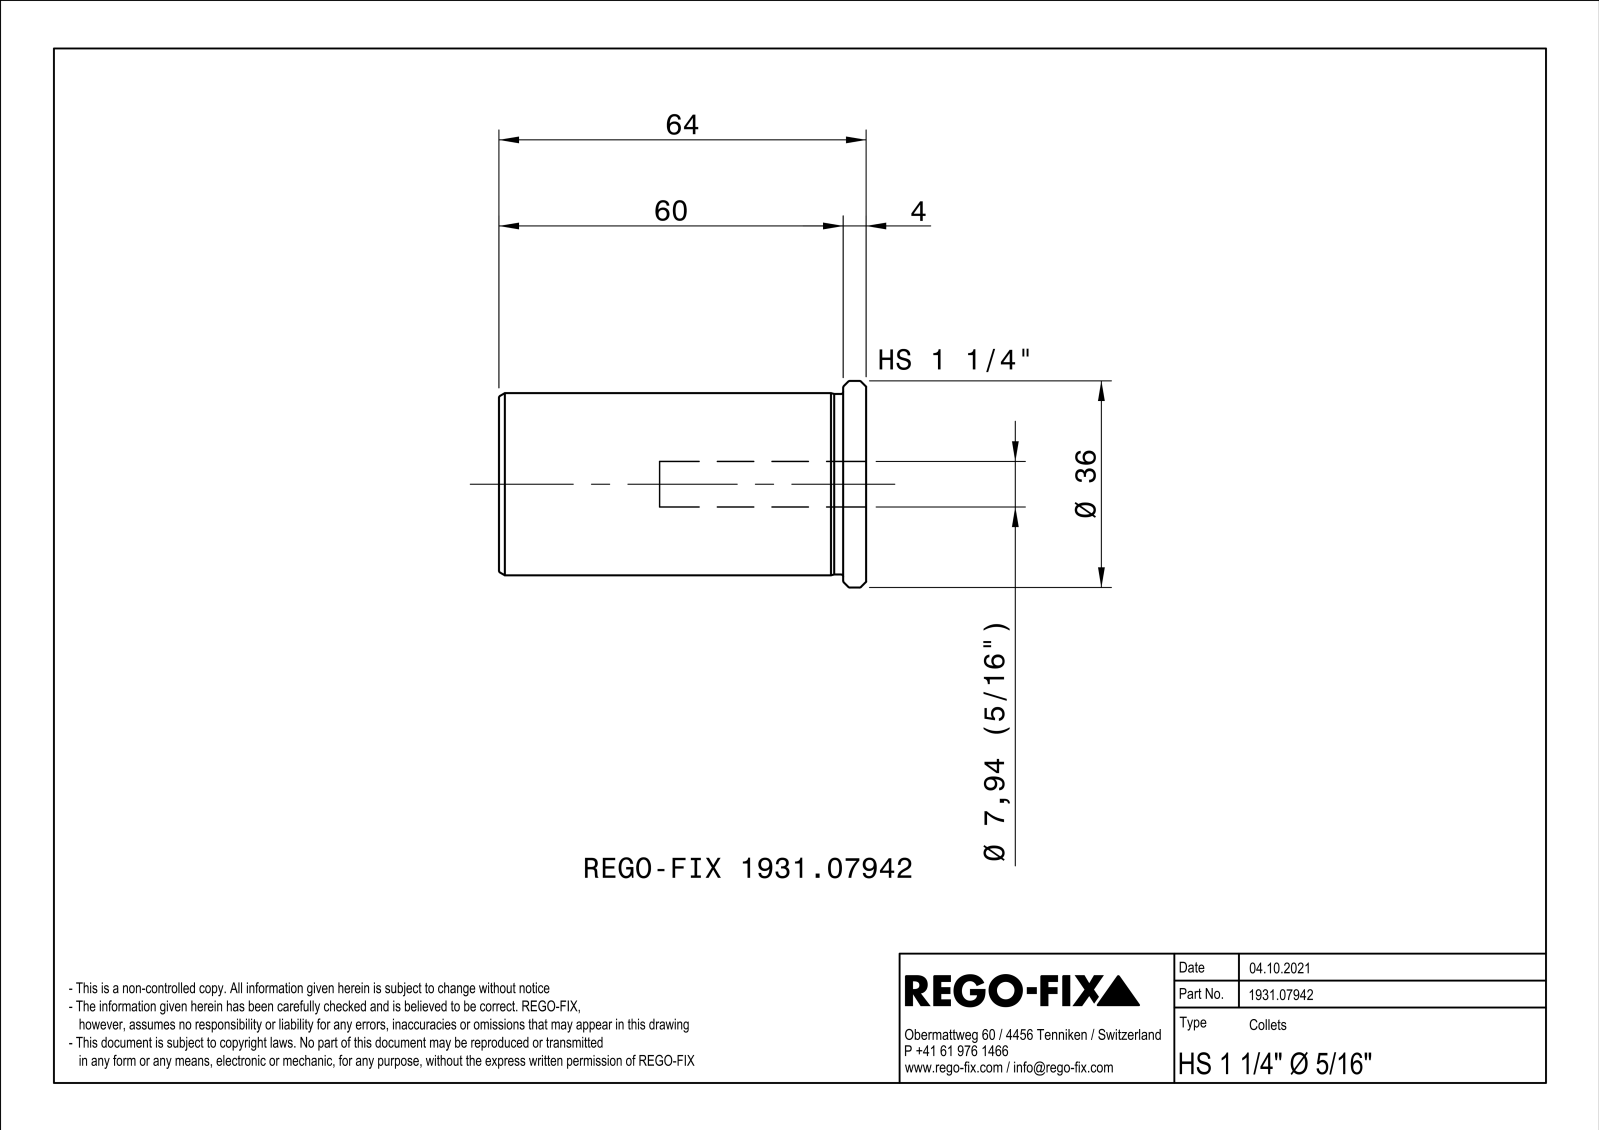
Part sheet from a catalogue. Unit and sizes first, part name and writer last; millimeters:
Units: millimetres
Overall size (bounding box): 64 × 35.99 × 35.99
Round holes (diameter × count): ⌀7.94 ×1, ⌀10 ×1, ⌀26.5 ×1
Round bosses / shafts (diameter × count): ⌀36 ×1, ⌀31.75 ×1, ⌀31.45 ×1
Main face-to-face distances: 1, 64, 4, 60
Volume: 38 329 mm³ · Surface area: 13 849 mm²
Bodies: 1 solid, 72 faces (22 planar, 12 cylindrical, 38 other)
Part name (STEP PRODUCT): NOCUT
STEP written by: SIEMENS PLM Software Solid Edge ST10 (AUTOMOTIVE_DESIGN)
